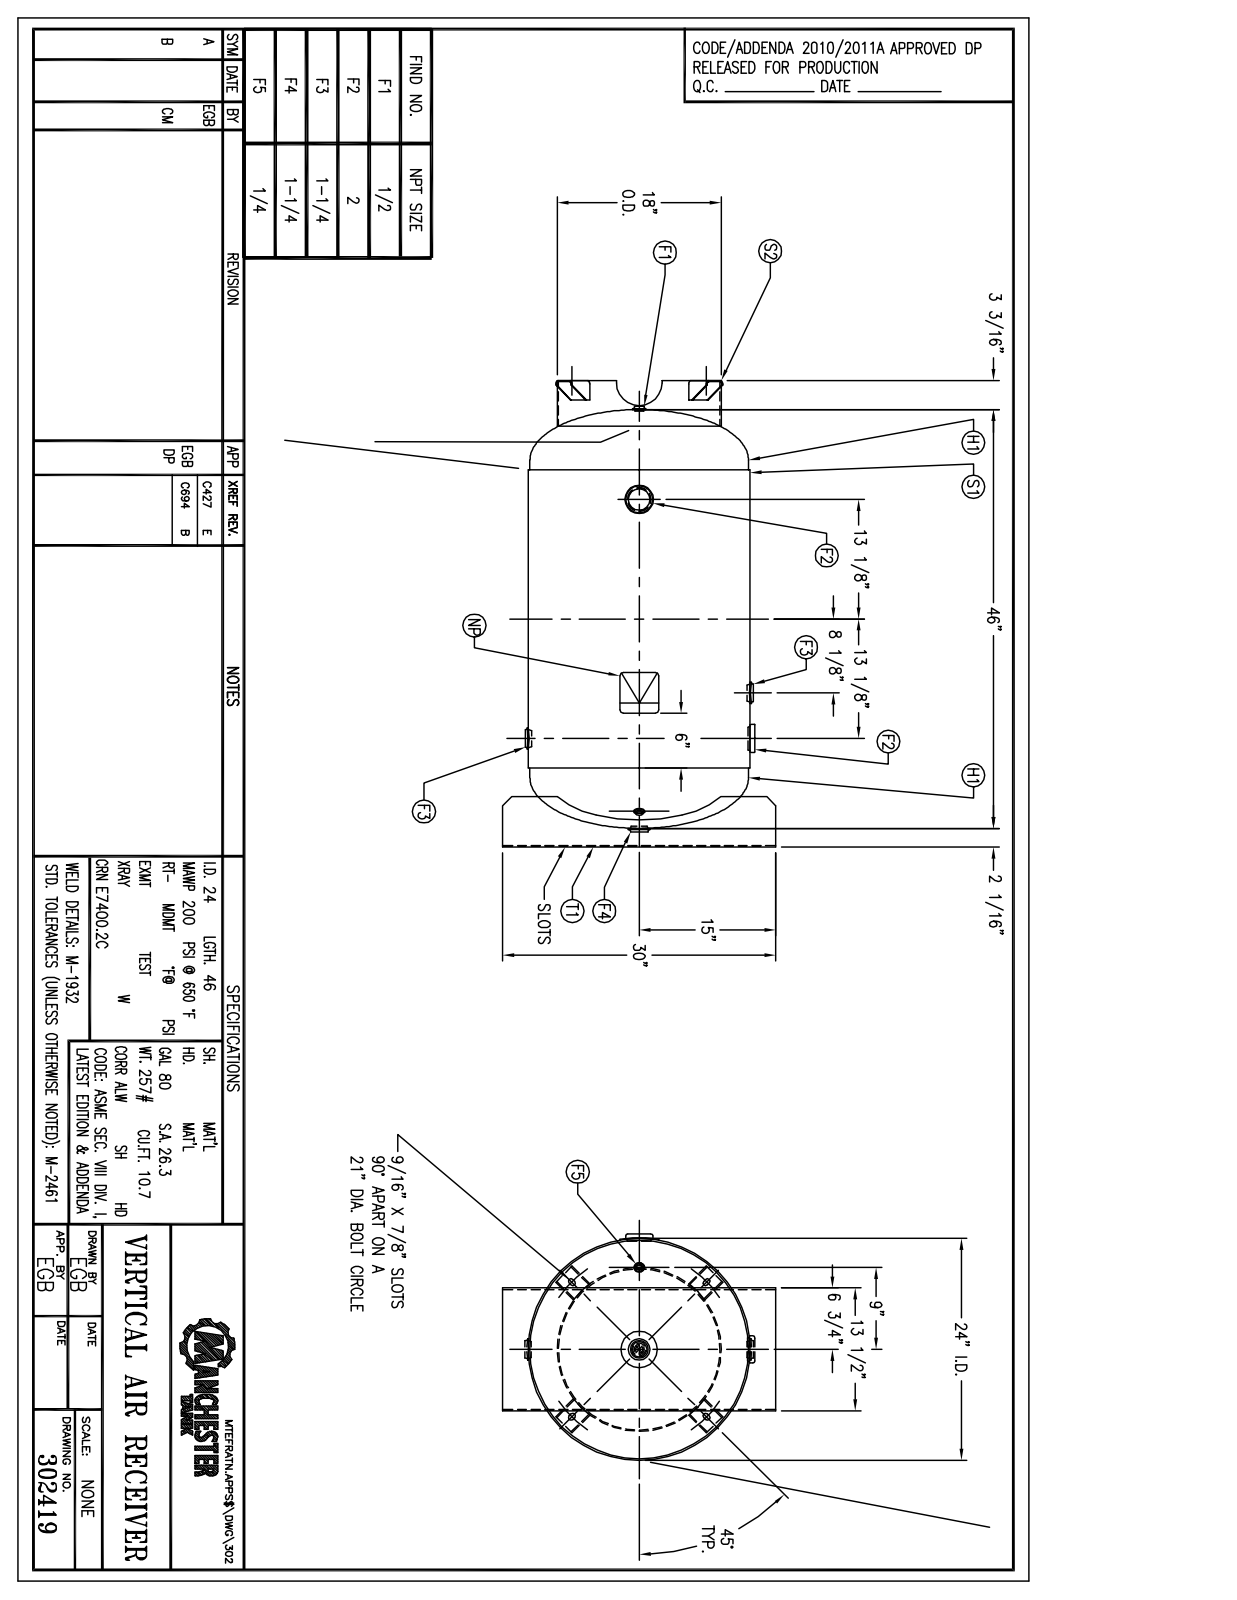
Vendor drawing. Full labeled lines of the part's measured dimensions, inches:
Part name (STEP PRODUCT): 302419
STEP written by: SolidWorks 2011 (CONFIG_CONTROL_DESIGN)
Units: inches
Bodies: 0 solids, 292 faces (136 planar, 94 cylindrical, 62 other)
Overall size (bounding box): 51.159 × 30 × 25.2
Round holes (diameter × count): ⌀1.66 ×3, ⌀2.375 ×2, ⌀0.54 ×1, ⌀0.84 ×1, ⌀4 ×1, ⌀17.732 ×1
Round bosses / shafts (diameter × count): ⌀3.625 ×2, ⌀2.125 ×2, ⌀1.45 ×2, ⌀1.438 ×2, ⌀24.368 ×1, ⌀24 ×1, ⌀18 ×1, ⌀1.062 ×1
Partial cylindrical surfaces — rounded edges, fillets, slot ends (radius × count): R0.203 ×20, R0.25 ×8, R0.281 ×8, R0.384 ×8, R0.254 ×2, R9.959 ×2, R0.075 ×1, R12.06 ×1
Main face-to-face distances: 0.179, 13.321, 13.5, 13.142, 0.134, 2.383, 51.159, 50.98, 51.025, 50.846
Hole centre spacings: 5
